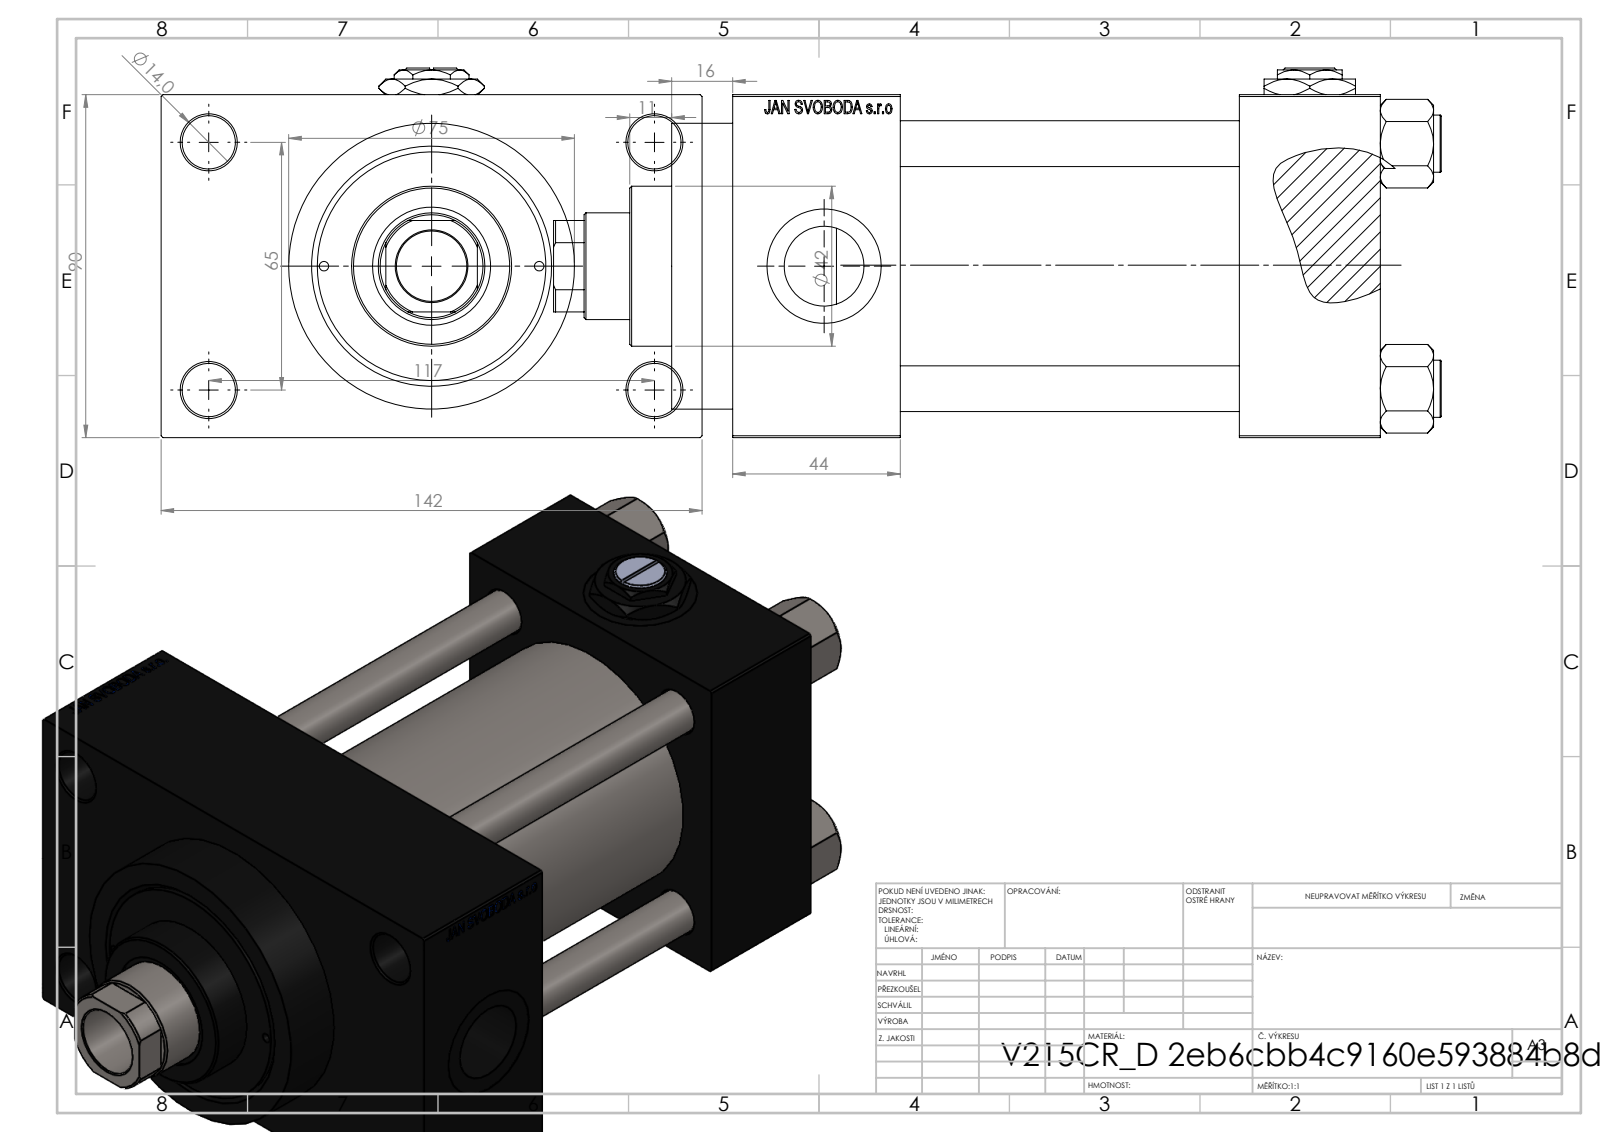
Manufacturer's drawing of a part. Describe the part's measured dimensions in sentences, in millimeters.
The part is named "V215CR_D_TYCINKA; Zatka_pro_OIL_PORT; NUT_M5_D; V215CR_D_Body (+2 more)". Its 3-D file was written by "SolidWorks 2019 (CONFIG_CONTROL_DESIGN)". It is 12 solids with 1164 faces: 523 planar, 99 cylindrical and 542 other. Overall it measures 233 by 142 by 97 millimeters. Its volume is 1 144 000 cubic millimeters and its surface area 222 605 square millimeters. Round holes: 4 of diameter 12, 4 of diameter 14, 3 of diameter 7, 3 of diameter 20.96, 3 of diameter 30, 2 of diameter 2.5, 1 of diameter 18.5, 1 of diameter 28, 1 of diameter 31, 1 of diameter 50, 1 of diameter 60, 1 of diameter 63. Round bosses or shafts: 4 of diameter 15, 1 of diameter 75, 1 of diameter 69, 1 of diameter 42. Partial cylindrical surfaces (rounded edges, fillets, slot ends): 1 of radius 13.5. The main face-to-face distances are 90, 89, 37, 126, 133, 170, 44, 116, 26, 142. The hole center spacings are 26.35, 32.39, 44.4, 45.47, 64.3, 66.92, 68.42, 69.81.
